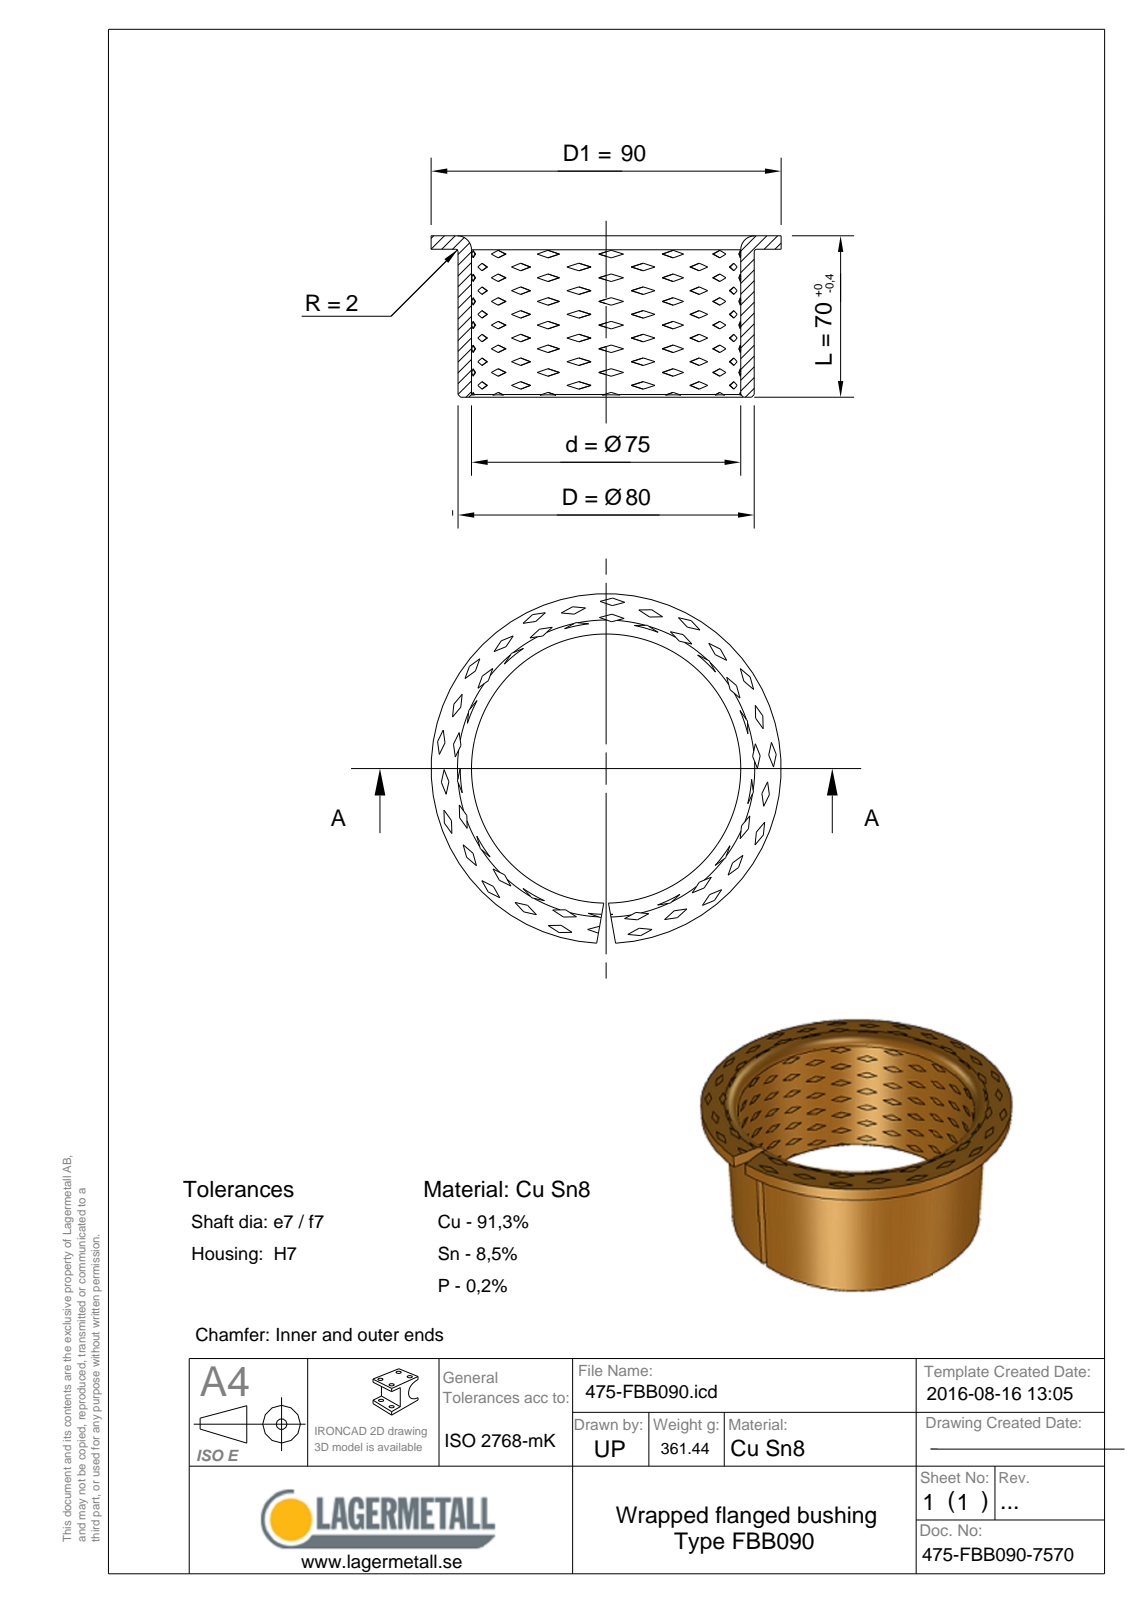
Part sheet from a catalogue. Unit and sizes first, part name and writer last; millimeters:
Units: millimetres
Overall size (bounding box): 90 × 89.97 × 70
Round holes (diameter × count): ⌀75 ×1
Round bosses / shafts (diameter × count): ⌀90 ×1, ⌀80 ×1
Main face-to-face distances: 2.5, 67.5, 70
Volume: 44 623 mm³ · Surface area: 37 296 mm²
Bodies: 1 solid, 12 faces (5 planar, 3 cylindrical, 4 other)
Part name (STEP PRODUCT): 475-FBB090-7570
STEP written by: Spatial InterOp 3D (CONFIG_CONTROL_DESIGN)
